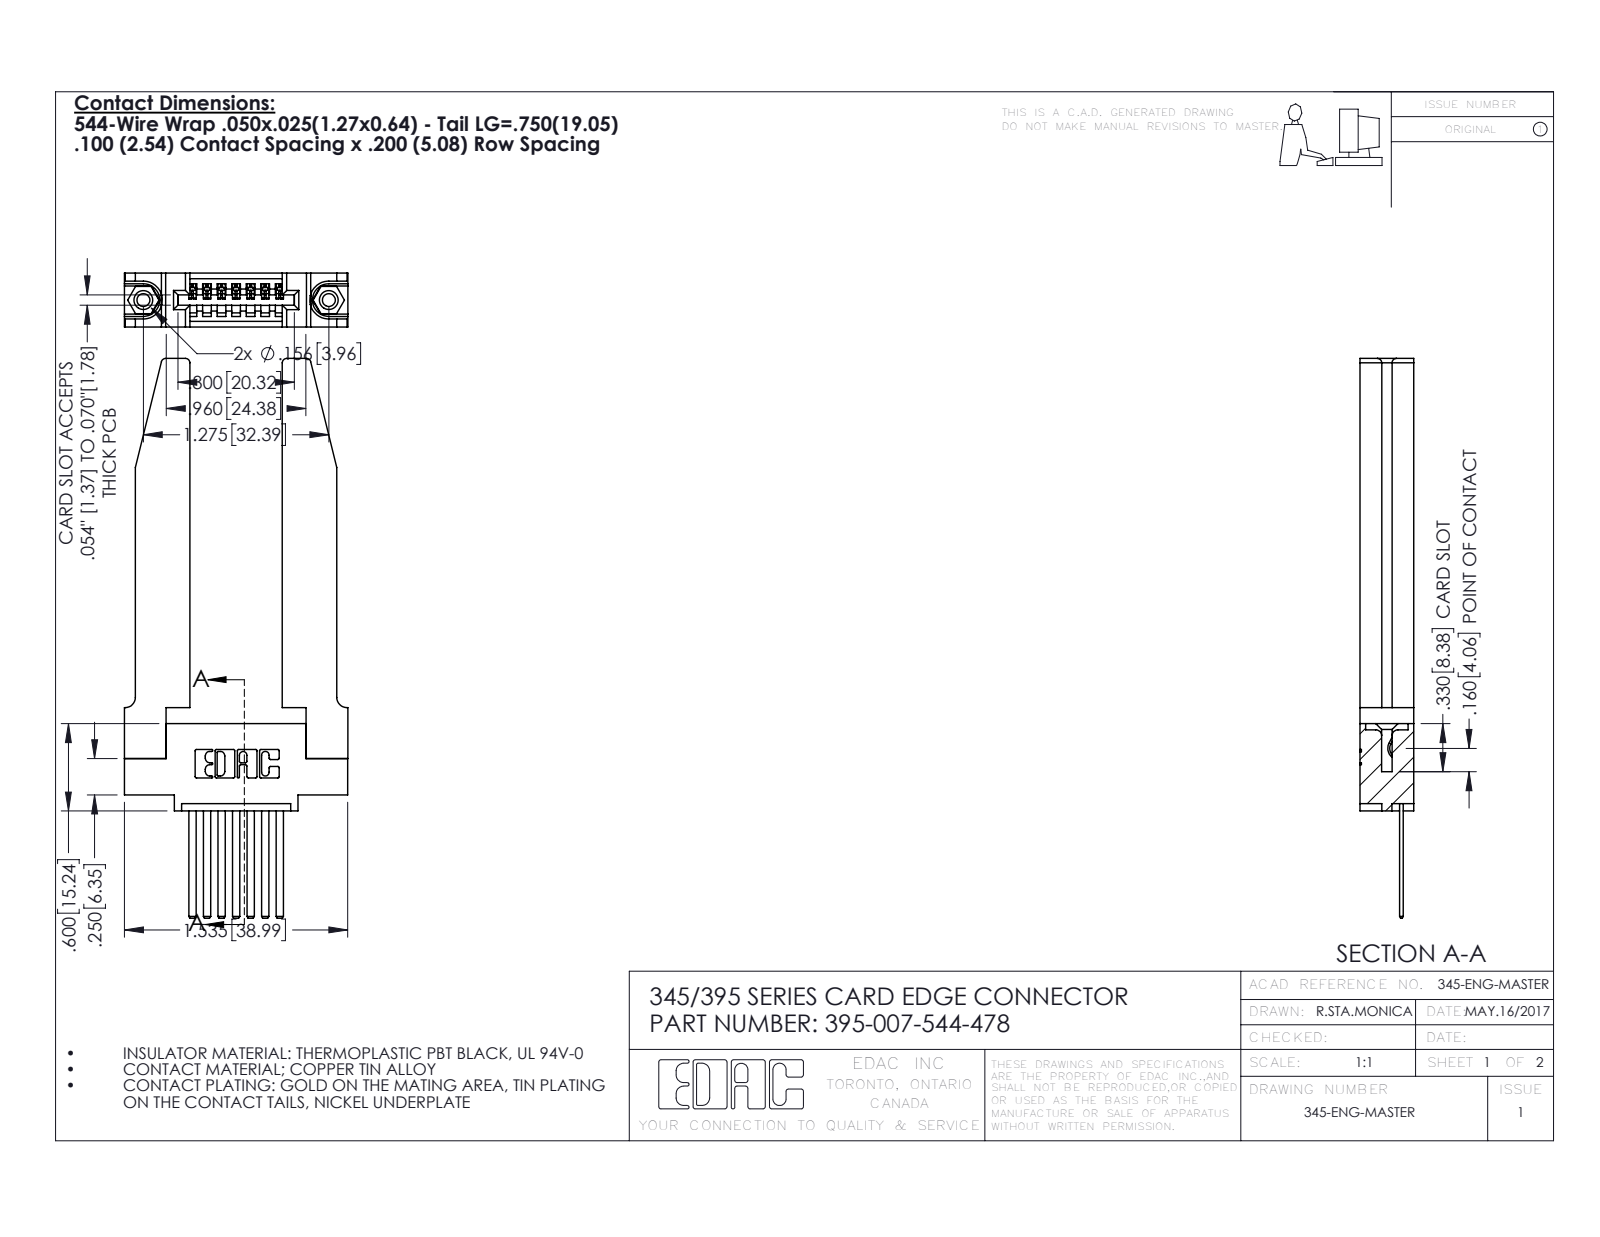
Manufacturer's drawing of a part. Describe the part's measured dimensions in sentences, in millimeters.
The part is named "345 Part_0.110 Offset - 0.156 Dia-TH; 345-220-078_345-220-078; 345-292-001_345-293-144; 395-007-544-478 (+1 more)". Its 3-D file was written by "SolidWorks 2016 (CONFIG_CONTROL_DESIGN)". It is 12 solids with 728 faces: 478 planar, 198 cylindrical and 52 other. Overall it measures 97.7 by 39 by 9.4 millimeters. Its volume is 11 200 cubic millimeters and its surface area 11 250 square millimeters. Round holes: 2 of diameter 2.3, 2 of diameter 3.2, 2 of diameter 4, 1 of diameter 1.6. Round bosses or shafts: 2 of diameter 3.9. Partial cylindrical surfaces (rounded edges, fillets, slot ends): 22 of radius 0.3, 14 of radius 0.2, 8 of radius 0.8, 6 of radius 0.2, 6 of radius 0.8, 3 of radius 0.7, 2 of radius 0.8, 2 of radius 1. The main face-to-face distances are 9.4, 1.8, 7.6, 3.8, 5.6, 3.8, 16.1, 2, 2.5, 6.9. The hole center spacings are 6.9, 26.5, 32.4.
